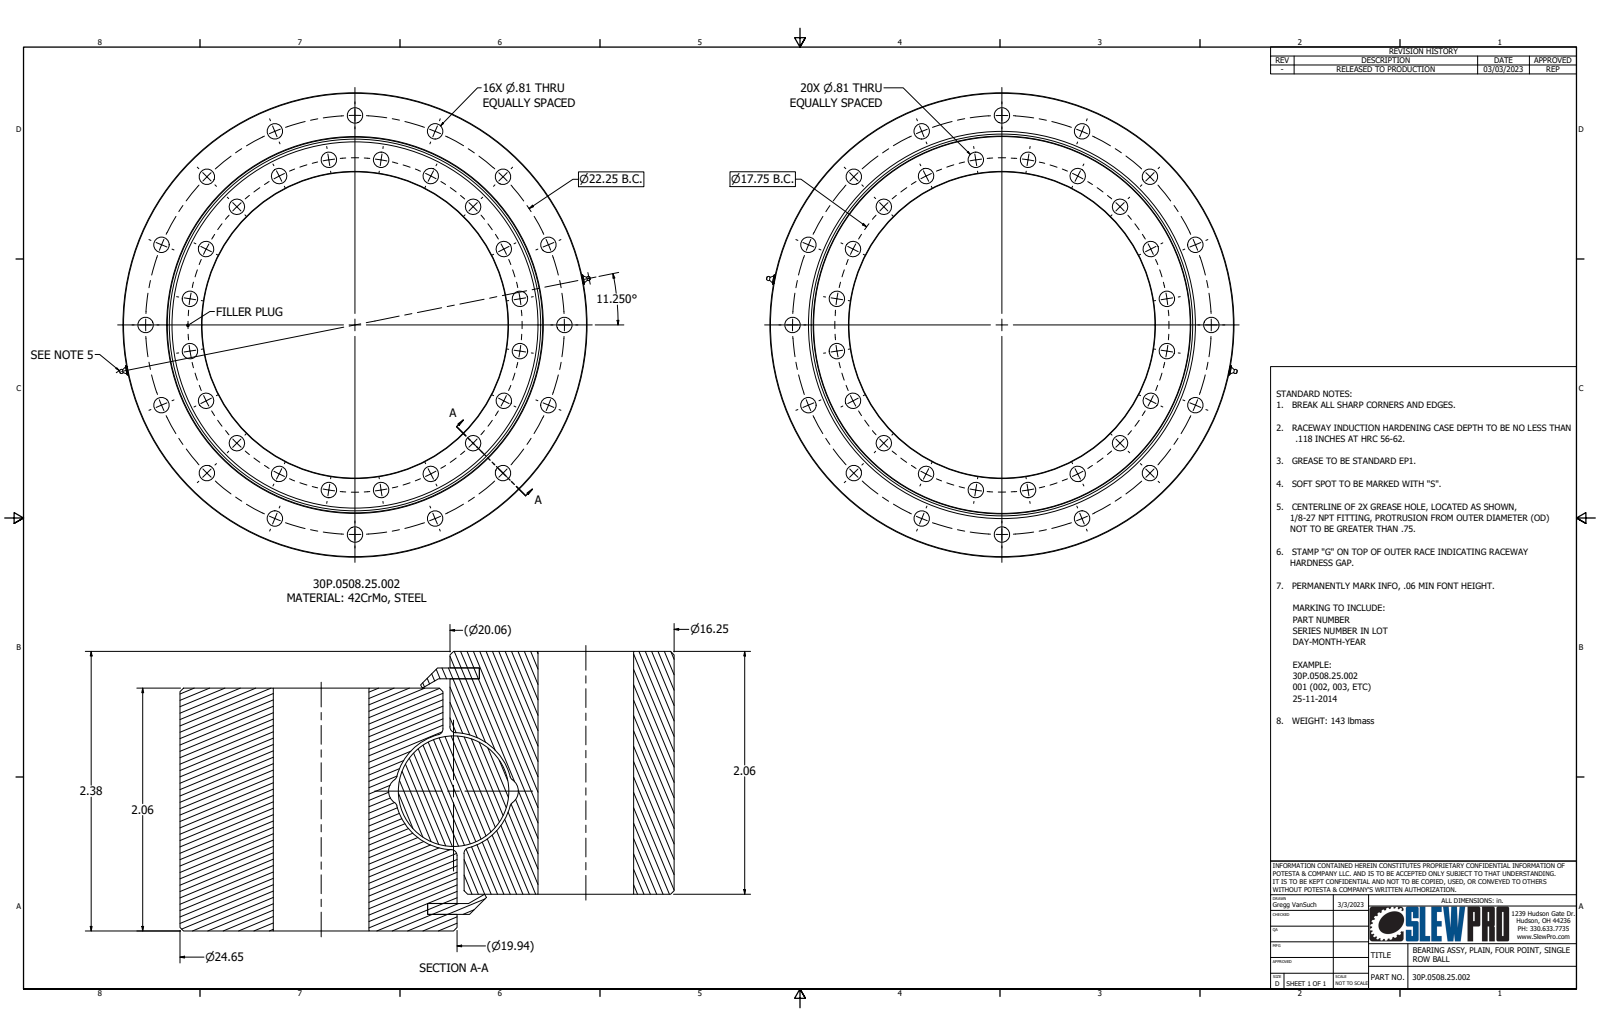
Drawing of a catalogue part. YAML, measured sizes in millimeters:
part_name: "30P.0508.25.002; 1_8 NPT Fitting"
step_written_by: "Autodesk Inventor 2026 (AUTOMOTIVE_DESIGN)"
units: millimeters
bodies: {solids: 8, faces: 270, planar: 36, cylindrical: 57, other: 177}
overall_size: [635.1, 626.1, 60.3]
volume: 8280000
surface_area: 1075000
round_holes:
  - {diameter: 20.7, count: 36}
  - {diameter: 2.5, count: 2}
  - {diameter: 28.2, count: 1}
  - {diameter: 412.8, count: 1}
  - {diameter: 496.8, count: 1}
  - {diameter: 506.5, count: 1}
  - {diameter: 512.6, count: 1}
  - {diameter: 519.2, count: 1}
round_bosses_or_shafts:
  - {diameter: 626.1, count: 1}
  - {diameter: 519.2, count: 1}
  - {diameter: 509.5, count: 1}
  - {diameter: 503.4, count: 1}
  - {diameter: 496.8, count: 1}
  - {diameter: 28.2, count: 1}
face_to_face_distances: [52.4, 7.9, 60.3, 44.5, 50.8, 2.4, 3.6, 56.7, 4.3, 48.8]
hole_center_spacings: [318.8, 445.3, 70.5, 265, 364.7, 401.7, 204.7, 225.4]
